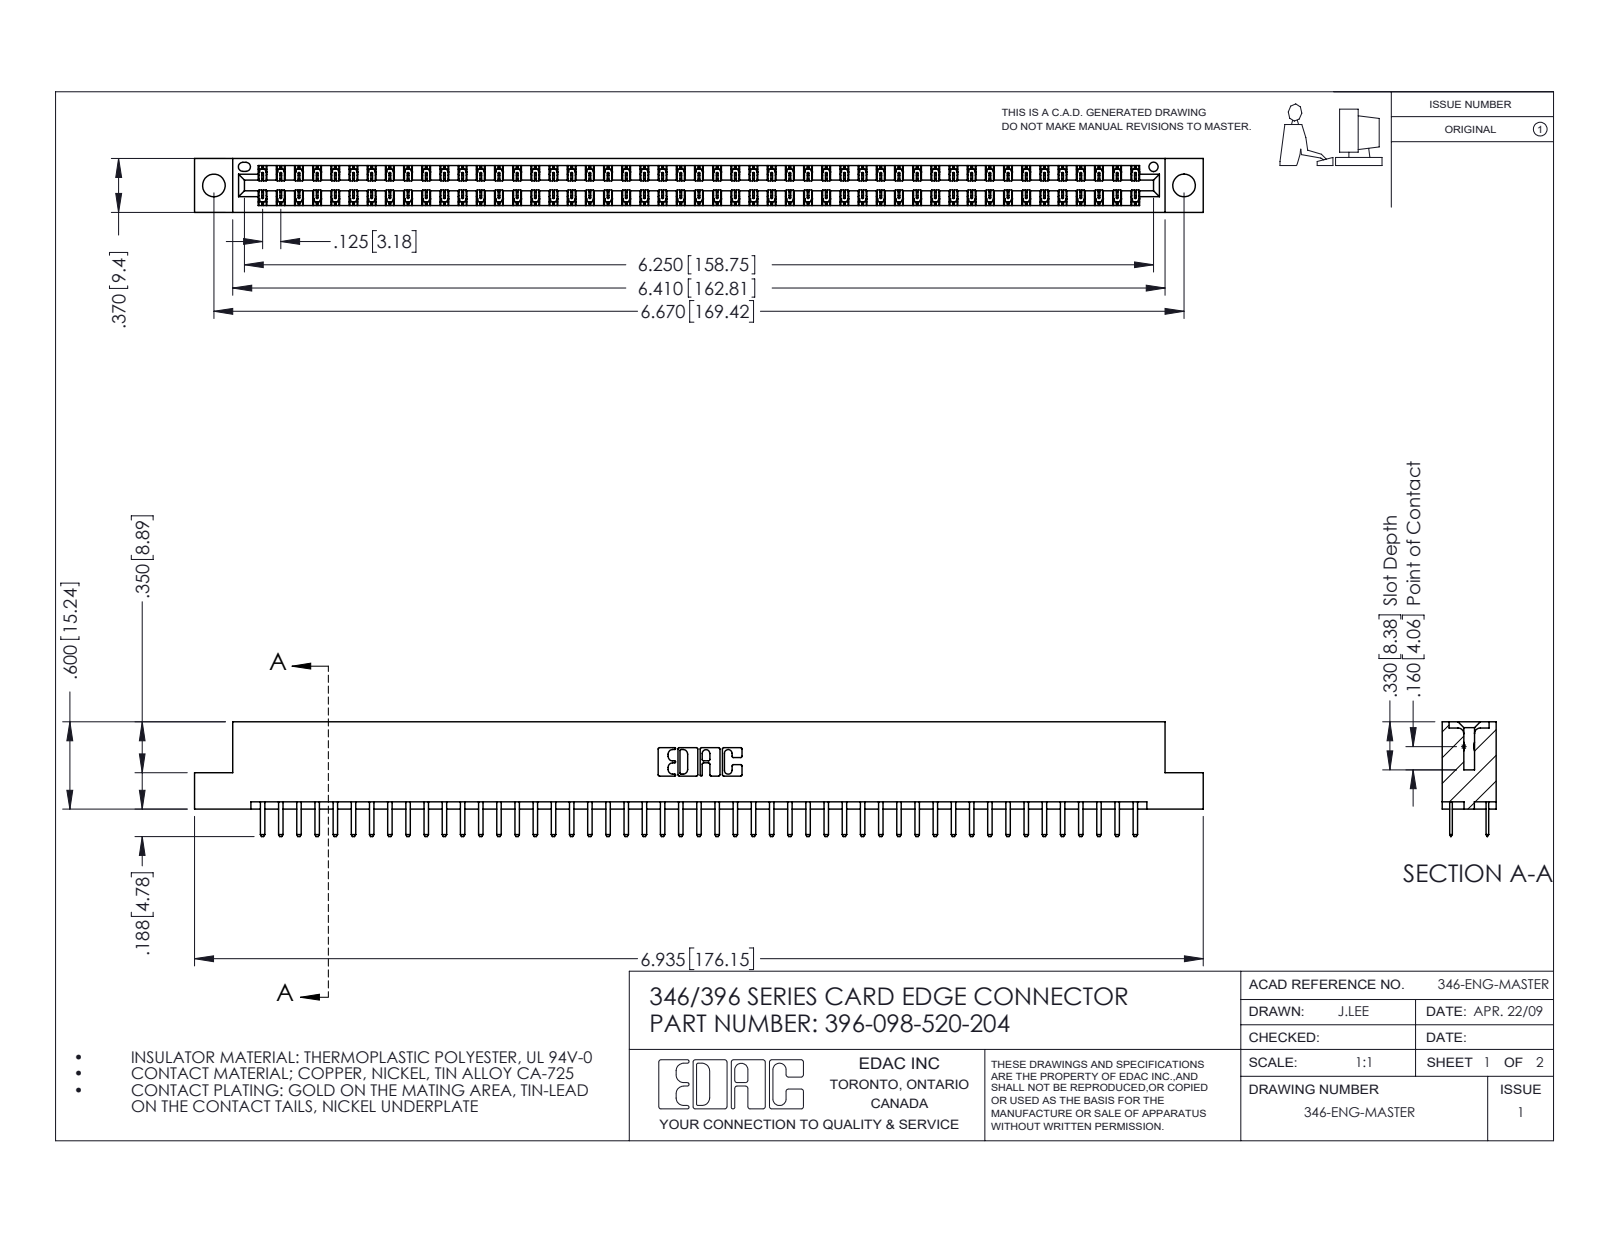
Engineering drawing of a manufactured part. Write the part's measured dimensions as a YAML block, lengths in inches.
part_name: "345-292-001_345-293-120; 346 Part_Flush Mounting Lugs - 0.156 Dia-TH; 396-098-520-204"
step_written_by: "SolidWorks 2016 (CONFIG_CONTROL_DESIGN)"
units: inches
bodies: {solids: 99, faces: 5610, planar: 3702, cylindrical: 1908, other: 0}
overall_size: [6.935, 0.788, 0.37]
volume: 1.044
surface_area: 36.16
round_holes:
  - {diameter: 0.156, count: 2}
  - {diameter: 0.064, count: 1}
partial_cylinders:
  - {radius: 0.006, count: 147}
  - {radius: 0.01, count: 102}
  - {radius: 0.01, count: 22}
  - {radius: 0.007, count: 6}
  - {radius: 0.031, count: 6}
  - {radius: 0.026, count: 3}
  - {radius: 0.014, count: 2}
  - {radius: 0.022, count: 2}
face_to_face_distances: [0.048, 0.322, 0.25, 0.37, 0.275, 0.072, 0.298, 0.025, 0.148, 0.222]
hole_center_spacings: [0.246, 6.461, 6.67]
